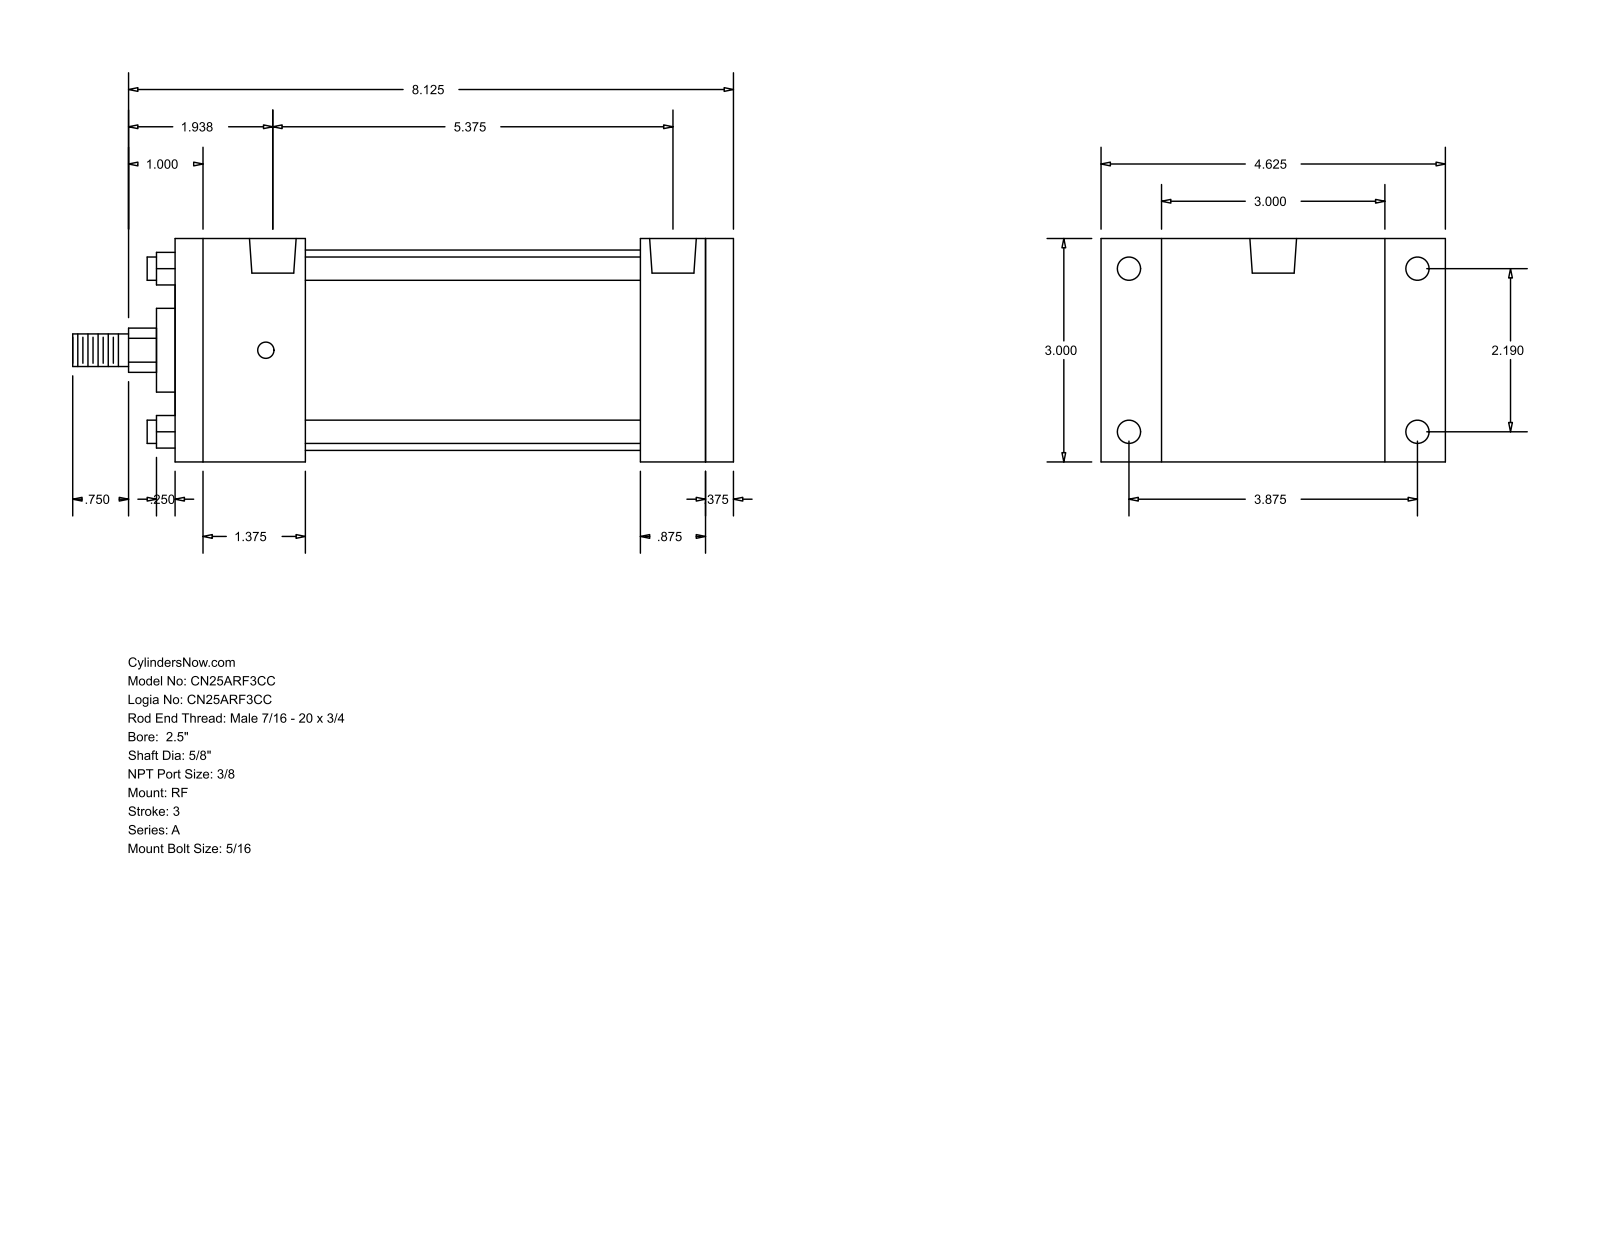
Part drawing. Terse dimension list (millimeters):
name: A_RF__0250_0.625
written by: GSSL Pune (CONFIG_CONTROL_DESIGN)
unit: mm
bodies: 0 solids, 92 faces (64 planar, 28 cylindrical, 0 other)
size: 225.43 × 117.47 × 76.2
holes: 4× ⌀5.56, 4× ⌀7.94, 2× ⌀15.93
bosses: 4× ⌀7.94, 1× ⌀68.33, 1× ⌀28.57, 1× ⌀15.88, 1× ⌀11.11
rounds: 1× R7.54
face distances: 76.2, 190.5, 9.53, 180.97, 44.45, 158.74, 114.29, 136.52, 146.05, 22.23
hole spacings: 2.38, 55.62, 98.42, 113.05, 138.91, 141.29, 136.53
